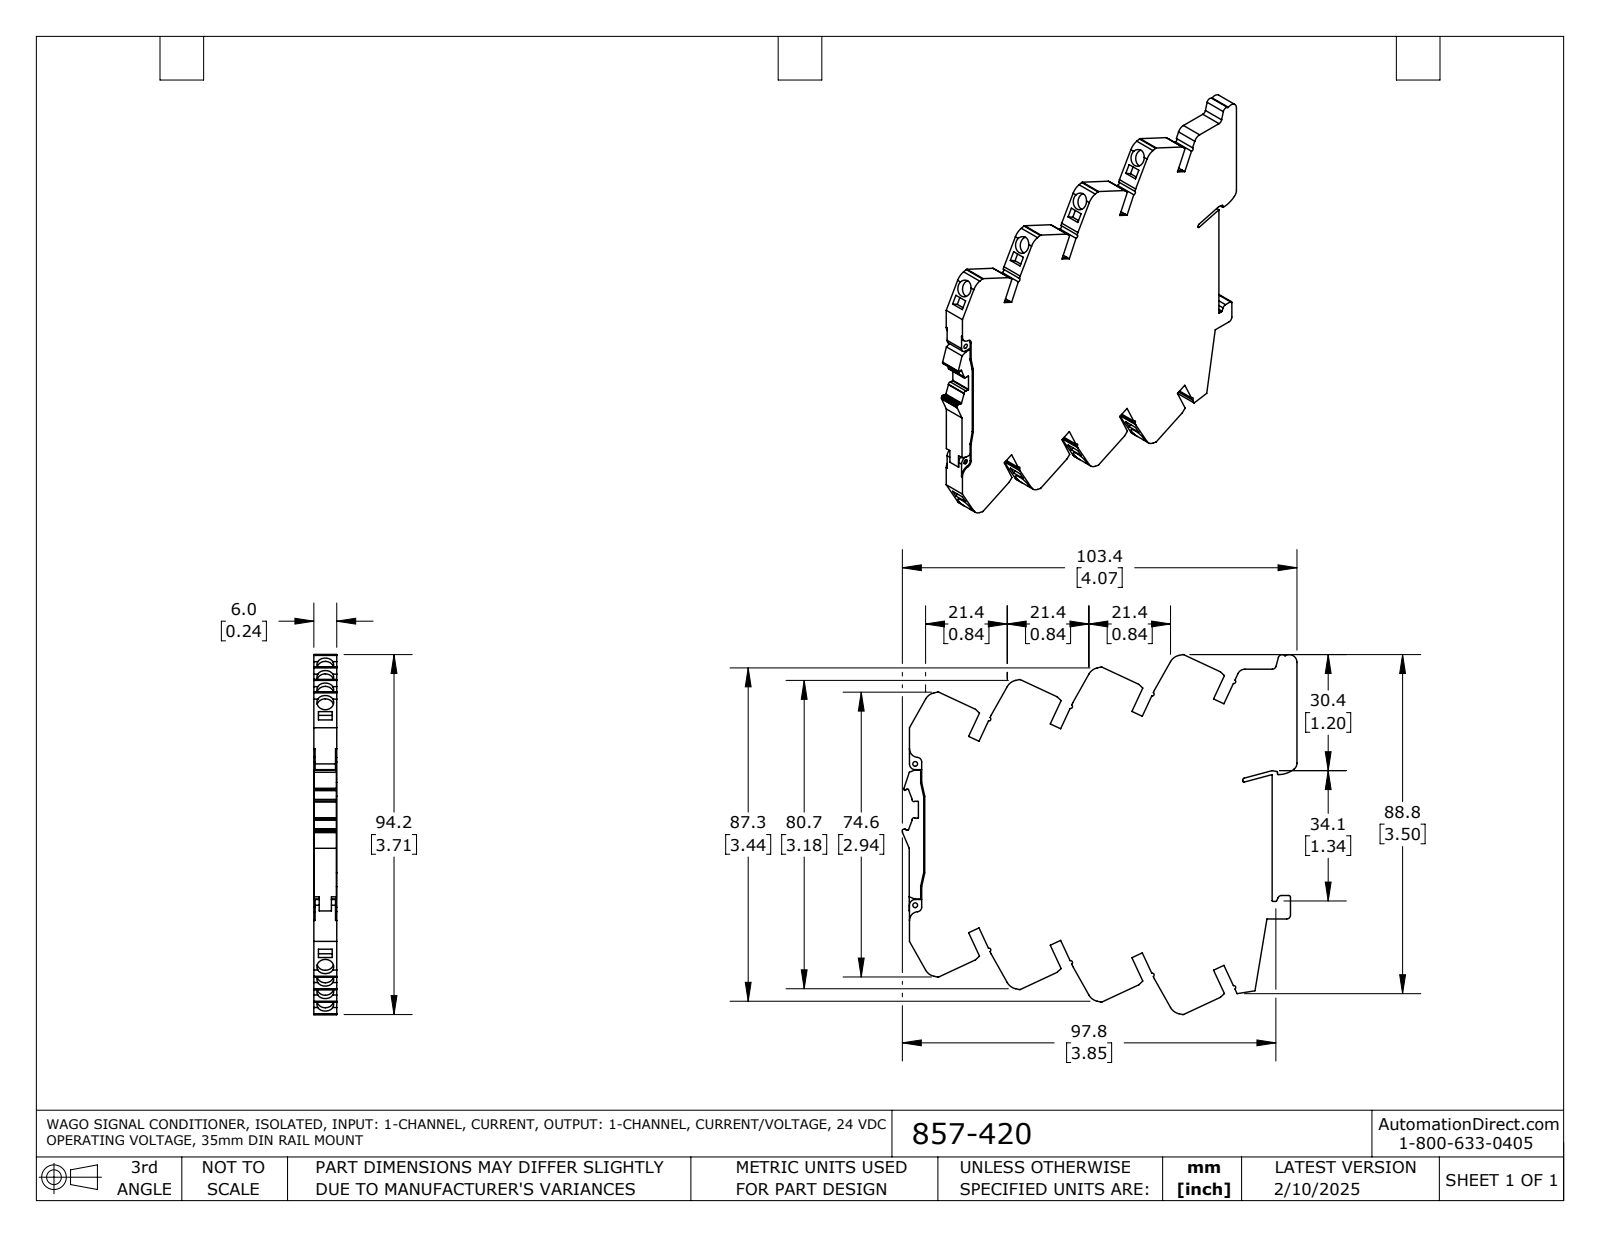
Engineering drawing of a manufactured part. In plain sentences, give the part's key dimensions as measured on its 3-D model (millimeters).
The part is named "857-420". Its 3-D file was written by "SolidWorks 2021 (AUTOMOTIVE_DESIGN)". It is 1 solid with 317 faces: 219 planar, 98 cylindrical and 0 other. Overall it measures 103.4 by 94.3 by 6 millimeters. Its volume is 43 930 cubic millimeters and its surface area 19 260 square millimeters. Round holes: 8 of diameter 4.4, 2 of diameter 1.2. Partial cylindrical surfaces (rounded edges, fillets, slot ends): 12 of radius 0.5, 11 of radius 0.2, 8 of radius 0.4, 8 of radius 3.4, 4 of radius 1, 3 of radius 0.3, 3 of radius 2, 2 of radius 0.5. The main face-to-face distances are 6, 18, 17, 12, 5.9, 12, 3, 24, 36, 6.5. The hole center spacings are 13.4, 13.3, 26.7, 26.7, 26.7, 37, 40, 40.1.
